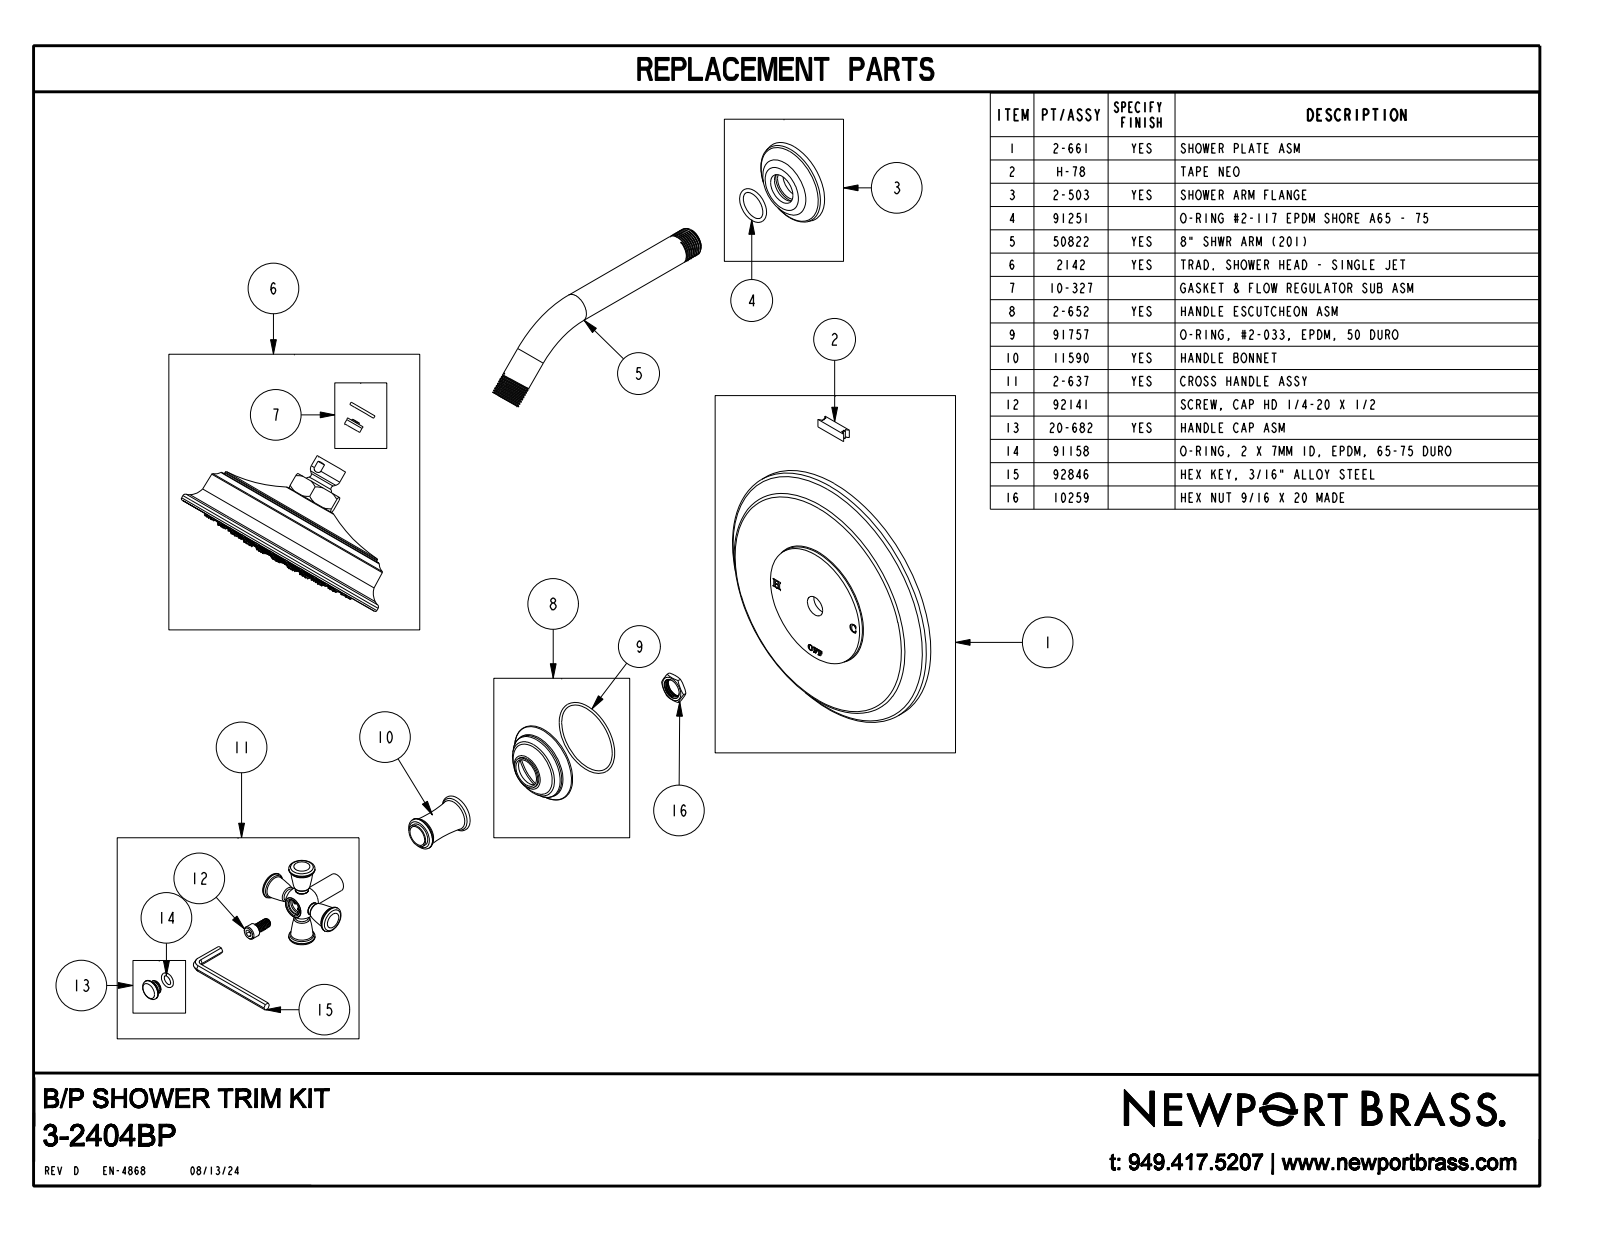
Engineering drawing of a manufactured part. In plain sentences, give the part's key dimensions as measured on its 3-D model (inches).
The part is named "3-2404BP". Its 3-D file was written by "CREO PARAMETRIC BY PTC INC, 2018400 (CONFIG_CONTROL_DESIGN)". It is 2 solids with 1283 faces: 269 planar, 240 cylindrical and 774 other. Overall it measures 16.935 by 10.691 by 7.5 inches. Its volume is 69.33 cubic inches and its surface area 232.3 square inches. Round holes: 90 of diameter 0.05, 1 of diameter 0.22, 1 of diameter 0.604, 1 of diameter 5.275. Round bosses or shafts: 2 of diameter 0.813, 2 of diameter 0.72, 2 of diameter 0.36, 1 of diameter 7.5, 1 of diameter 6.2, 1 of diameter 5.22, 1 of diameter 4.83, 1 of diameter 1.42. The main face-to-face distances are 0.625, 0.125, 0.75, 0.48, 0.145, 0.27, 1.014, 1.011, 2.025, 2.986. The hole center spacings are 0.48, 1.84, 1.84, 2.27, 0.952, 1.408, 0.474, 2.24.
